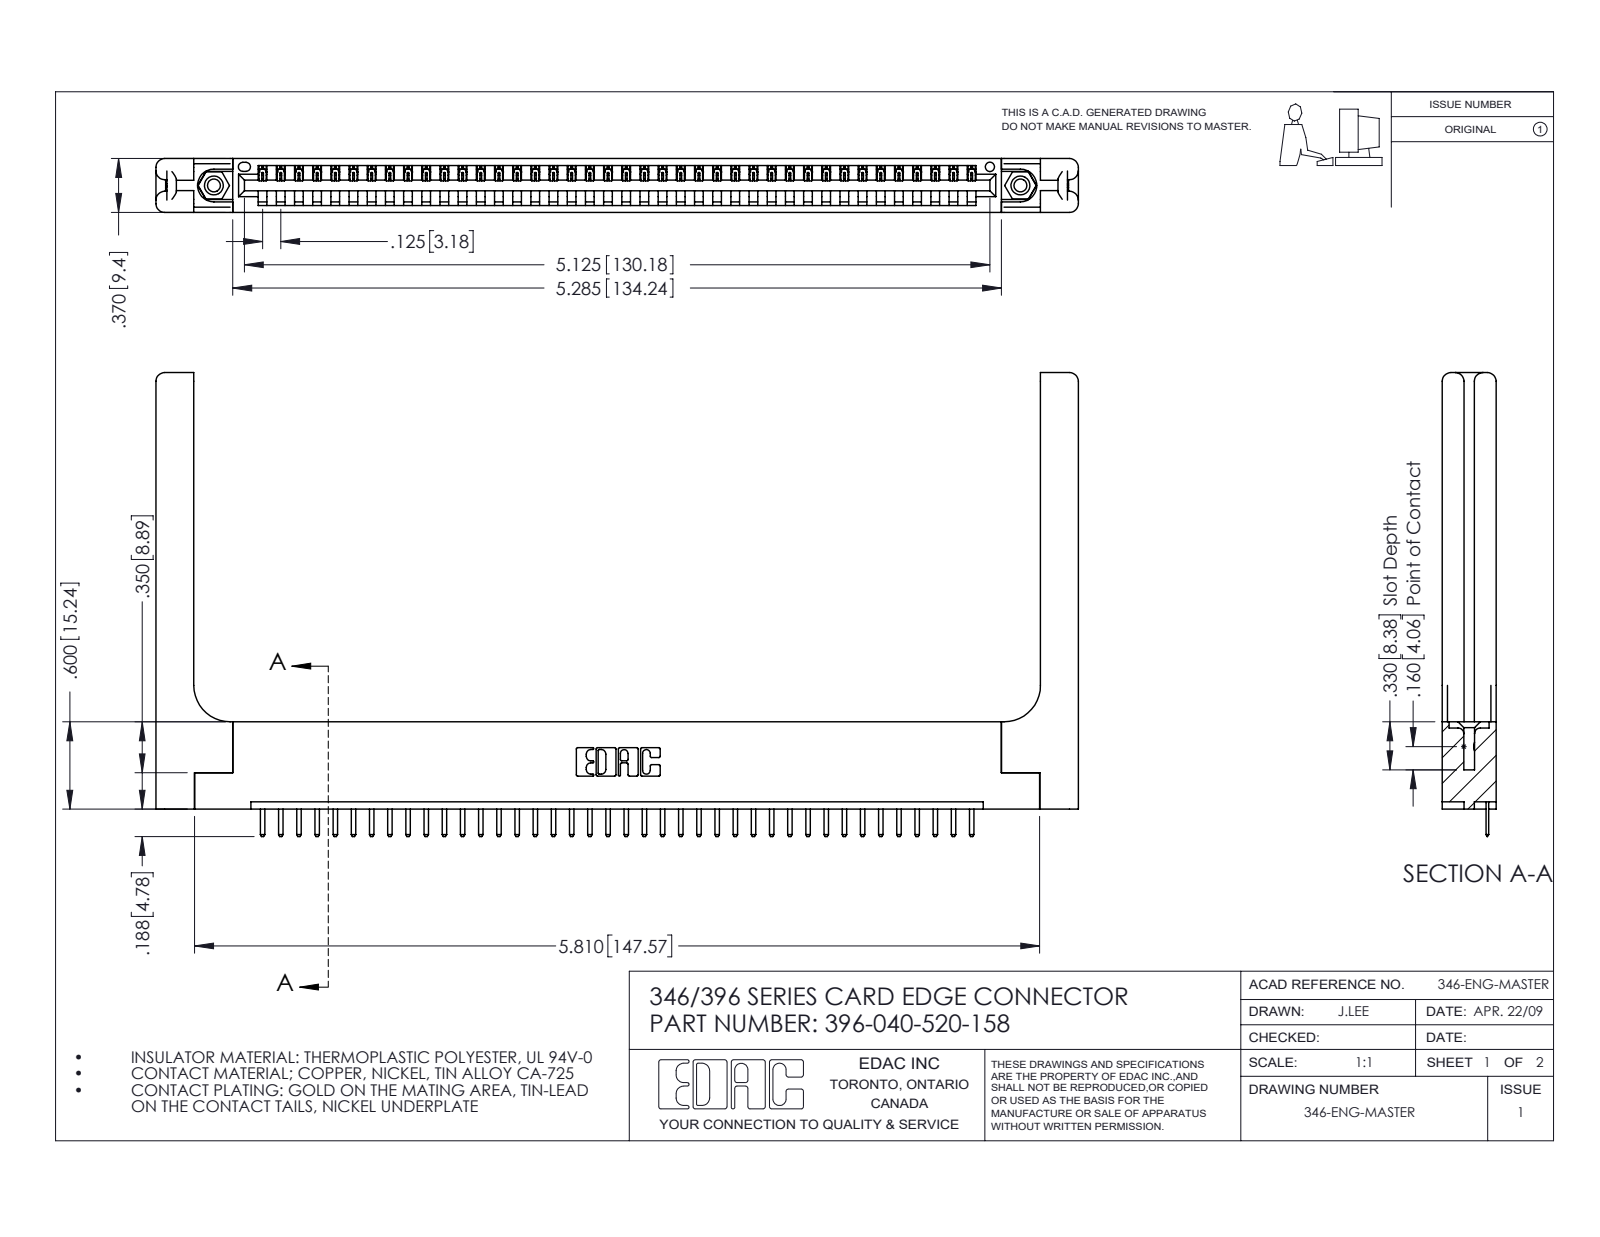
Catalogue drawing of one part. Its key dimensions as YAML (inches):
part_name: "346 Part_Flush Mounting Lugs - 0.156 Dia-TH; 396-040-520-158; 345-250-001_345-250-001-102; 346-220-058_345-220-058 (+1 more)"
step_written_by: "SolidWorks 2016 (CONFIG_CONTROL_DESIGN)"
units: inches
bodies: {solids: 45, faces: 2858, planar: 1904, cylindrical: 894, other: 60}
overall_size: [6.341, 3.188, 0.37]
volume: 1.392
surface_area: 37
round_holes:
  - {diameter: 0.089, count: 2}
  - {diameter: 0.125, count: 2}
  - {diameter: 0.156, count: 2}
  - {diameter: 0.064, count: 1}
round_bosses_or_shafts:
  - {diameter: 0.155, count: 2}
partial_cylinders:
  - {radius: 0.01, count: 82}
  - {radius: 0.006, count: 80}
  - {radius: 0.01, count: 22}
  - {radius: 0.06, count: 16}
  - {radius: 0.007, count: 6}
  - {radius: 0.031, count: 6}
  - {radius: 0.026, count: 3}
  - {radius: 0.03, count: 2}
face_to_face_distances: [0.37, 0.048, 0.322, 0.072, 0.148, 0.15, 0.25, 0.298, 0.025, 0.222]
hole_center_spacings: [0.246, 5.336, 5.545]
